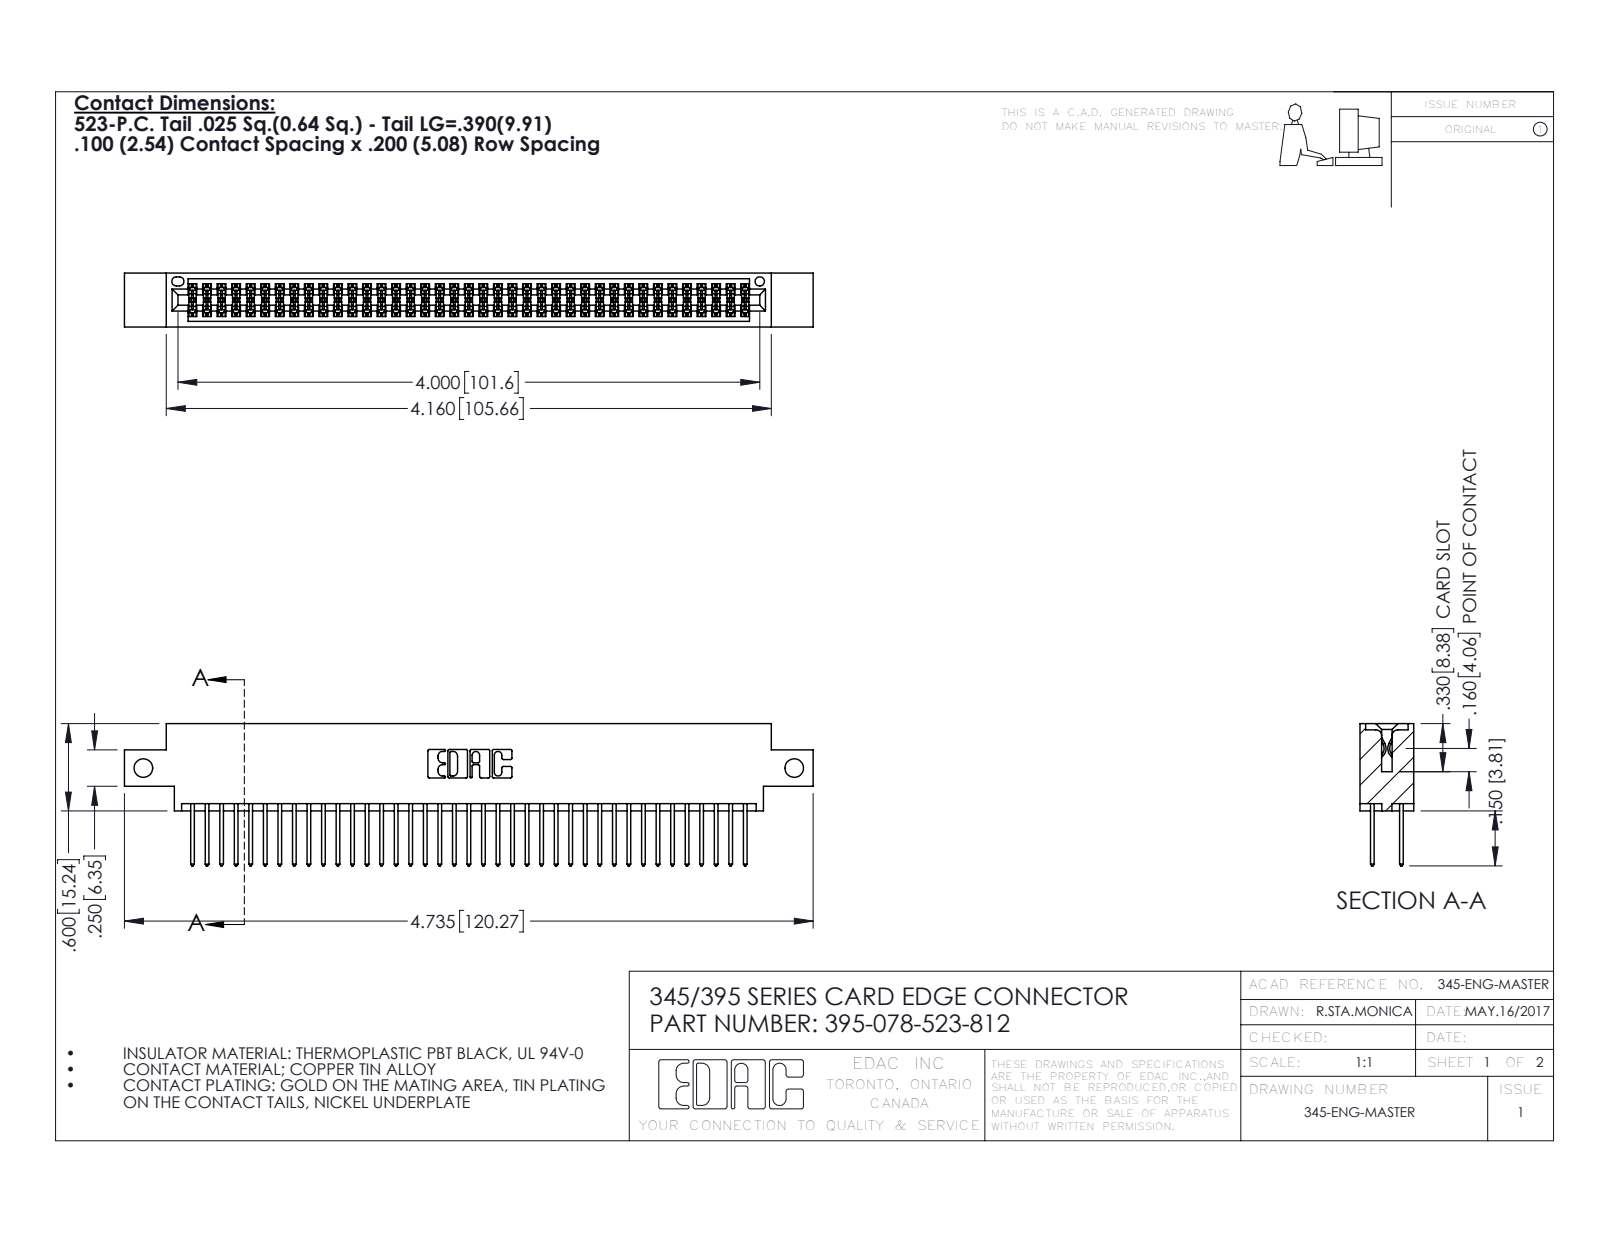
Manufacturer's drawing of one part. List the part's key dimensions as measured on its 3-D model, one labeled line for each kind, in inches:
Part name (STEP PRODUCT): 345 Part_0.170 Offset - Side Mount; 395-078-523-812; 345-292-001_345-293-123
STEP written by: SolidWorks 2016 (CONFIG_CONTROL_DESIGN)
Units: inches
Bodies: 79 solids, 4030 faces (2658 planar, 1372 cylindrical, 0 other)
Overall size (bounding box): 4.735 × 0.977 × 0.37
Volume: 0.709 in³ · Surface area: 27.64 in²
Round holes (diameter × count): ⌀0.128 ×2, ⌀0.064 ×1
Partial cylindrical surfaces — rounded edges, fillets, slot ends (radius × count): R0.006 ×117, R0.01 ×78, R0.01 ×22, R0.007 ×6, R0.031 ×6, R0.026 ×3, R0.014 ×2, R0.019 ×2
Main face-to-face distances: 0.298, 0.072, 0.2, 0.098, 0.272, 0.025, 0.37, 0.225, 0.175, 0.149
Hole centre spacings: 4.475
